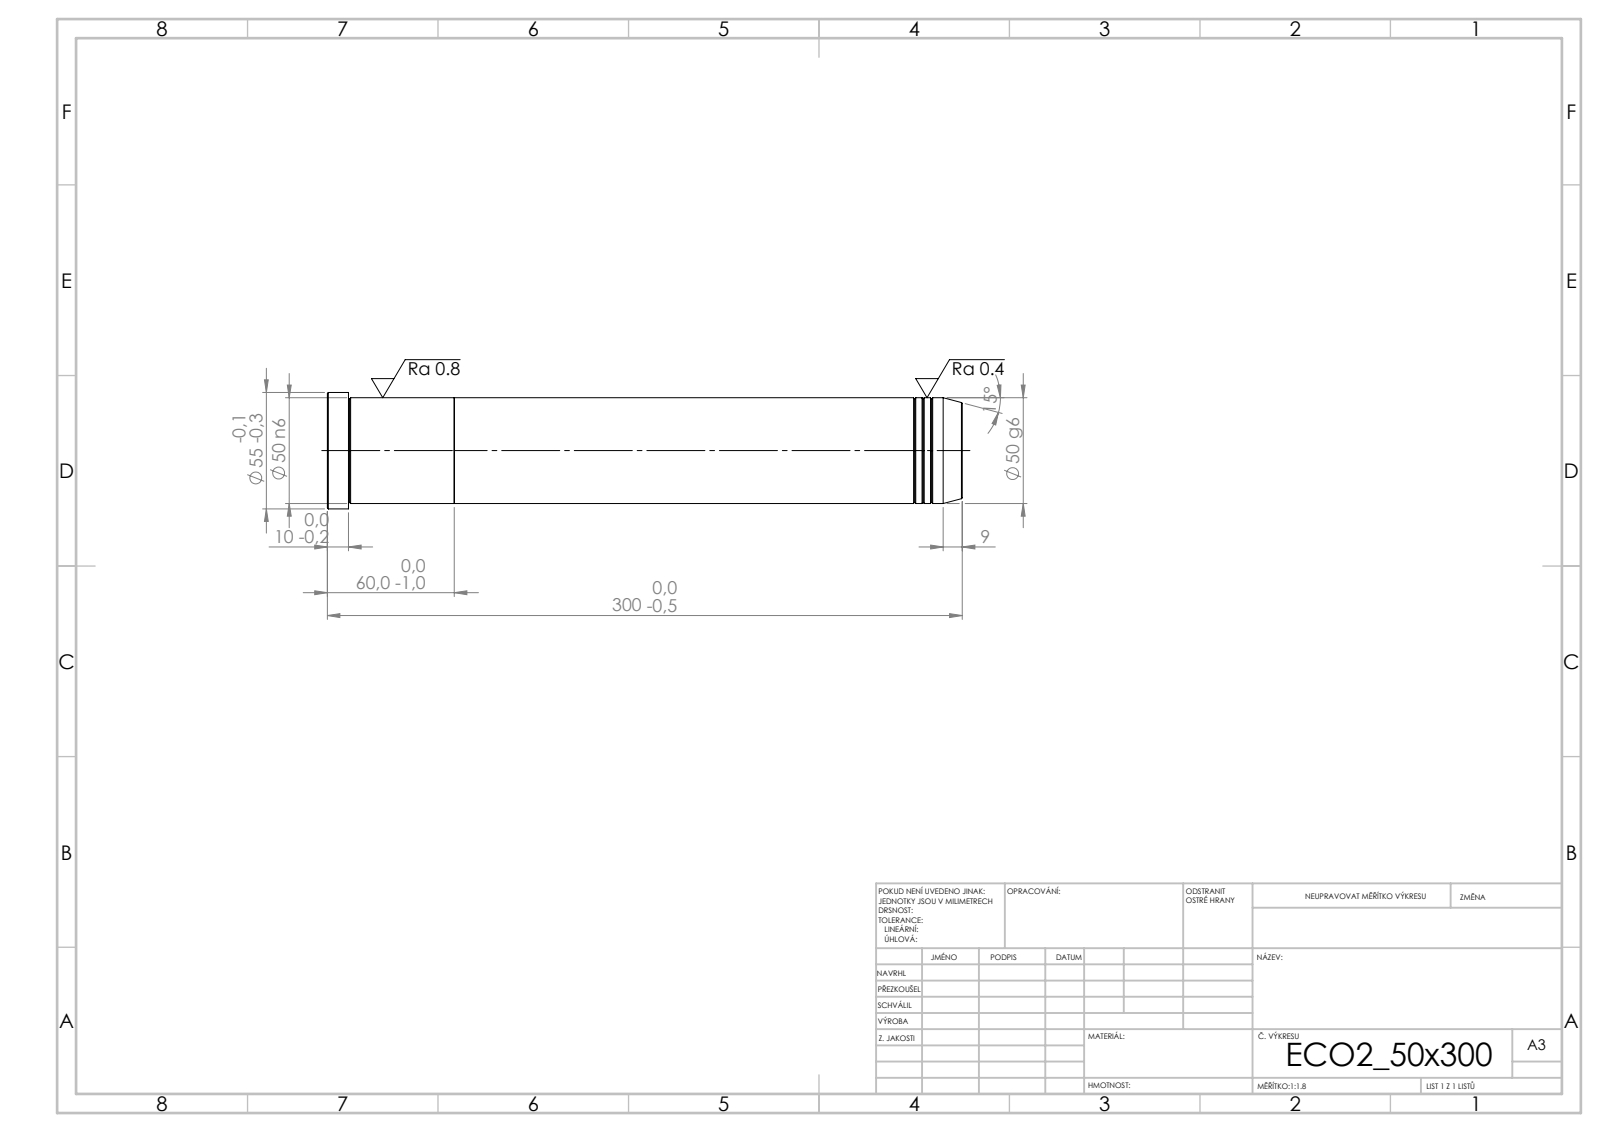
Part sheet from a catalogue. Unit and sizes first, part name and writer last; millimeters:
Units: millimetres
Overall size (bounding box): 300 × 55 × 55
Round bosses / shafts (diameter × count): ⌀55 ×1, ⌀50 ×1
Main face-to-face distances: 60, 240, 300, 290, 50, 10
Volume: 591 252 mm³ · Surface area: 55 857 mm²
Bodies: 2 solids, 39 faces (5 planar, 12 cylindrical, 22 other)
STEP written by: SolidWorks 2019 (CONFIG_CONTROL_DESIGN)
